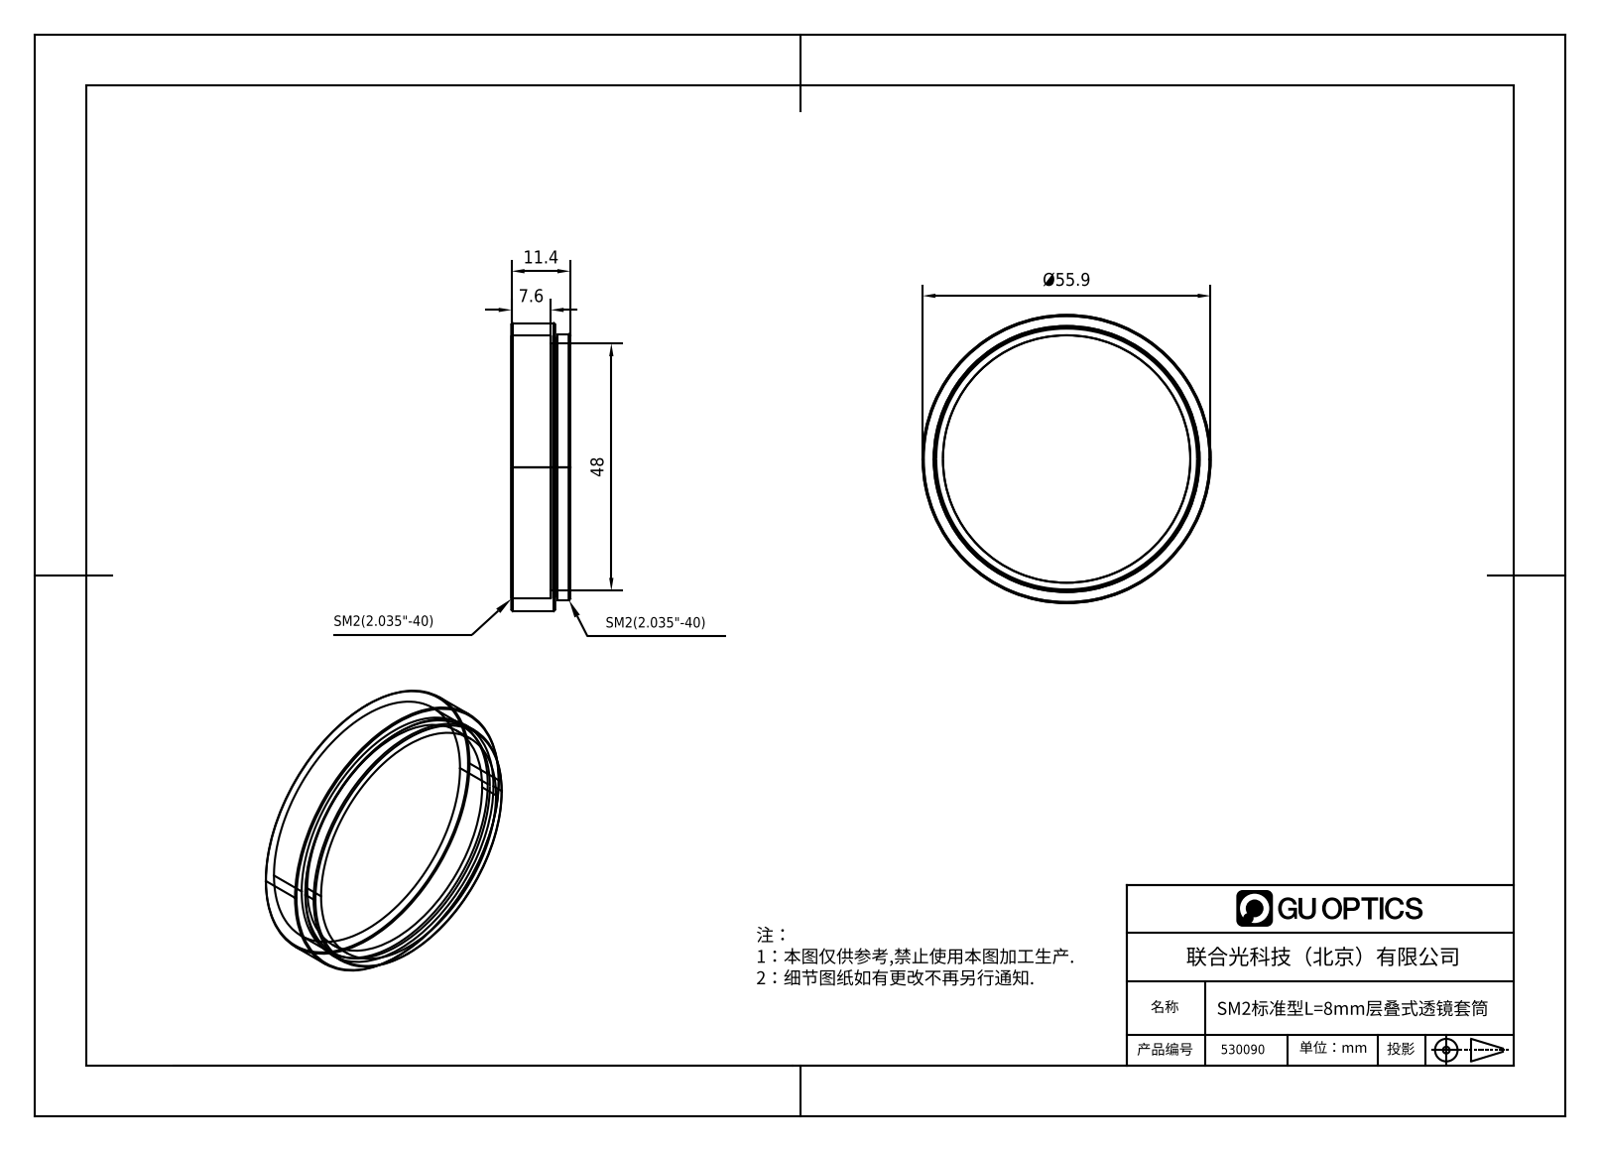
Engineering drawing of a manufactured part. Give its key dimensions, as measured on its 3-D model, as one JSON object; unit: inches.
{"part_name": "1.7.1.16_ZTC-2-0.3_SM2标准型0.3英寸层叠式透镜套筒", "step_written_by": "SolidWorks 2018 (AUTOMOTIVE_DESIGN)", "units": "inches", "bodies": {"solids": 0, "faces": 36, "planar": 13, "cylindrical": 12, "other": 11}, "overall_size": [2.201, 2.201, 0.449], "round_holes": [[1.878, 1], [1.89, 1], [2.01, 1]], "round_bosses_or_shafts": [[2.201, 1], [2.031, 1], [1.992, 1]], "face_to_face_distances": [0.331, 0.449, 0.118, 0.299, 0.031, 0.15, 0.117, 0.182, 0.214, 0.332]}
